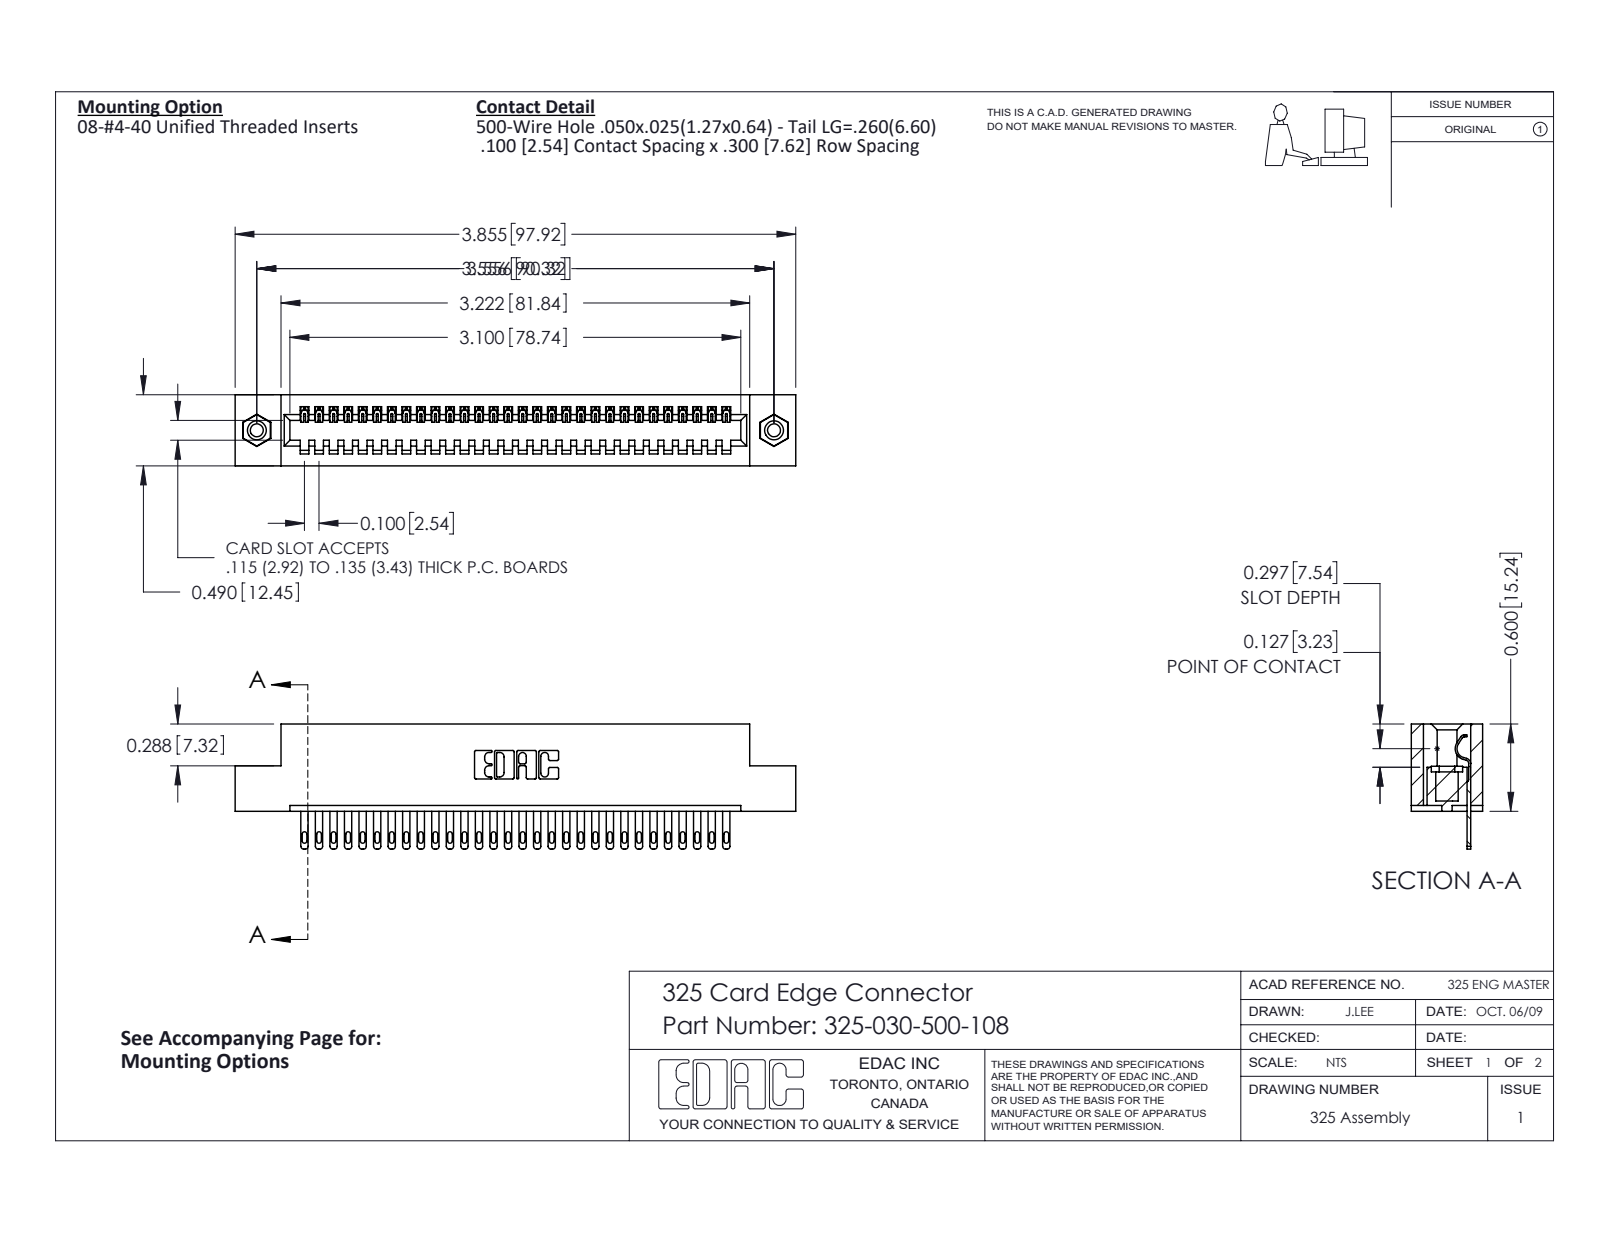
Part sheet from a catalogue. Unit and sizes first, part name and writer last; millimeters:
Units: millimetres
Overall size (bounding box): 97.9 × 21.8 × 12.4
Round holes (diameter × count): ⌀2.3 ×2, ⌀3.2 ×2, ⌀4.1 ×2
Round bosses / shafts (diameter × count): ⌀3.9 ×2
Partial cylindrical surfaces — rounded edges, fillets, slot ends (radius × count): R0.2 ×60, R0.4 ×60, R0.5 ×60, R0.3 ×22, R0.2 ×6, R0.8 ×6, R0.7 ×3, R0.4 ×1
Main face-to-face distances: 2.1, 10.3, 12.4, 7.6, 2.7, 9.7, 0.6, 8.3, 1, 14.2
Hole centre spacings: 90.3
Volume: 12 400 mm³ · Surface area: 13 370 mm²
Bodies: 33 solids, 1794 faces (1182 planar, 596 cylindrical, 16 other)
Part name (STEP PRODUCT): 325-030-500-108; 345-250-001_345-250-003-102; 325-292-001_325-293-100; 325 Part_TI
STEP written by: SolidWorks 2016 (CONFIG_CONTROL_DESIGN)
